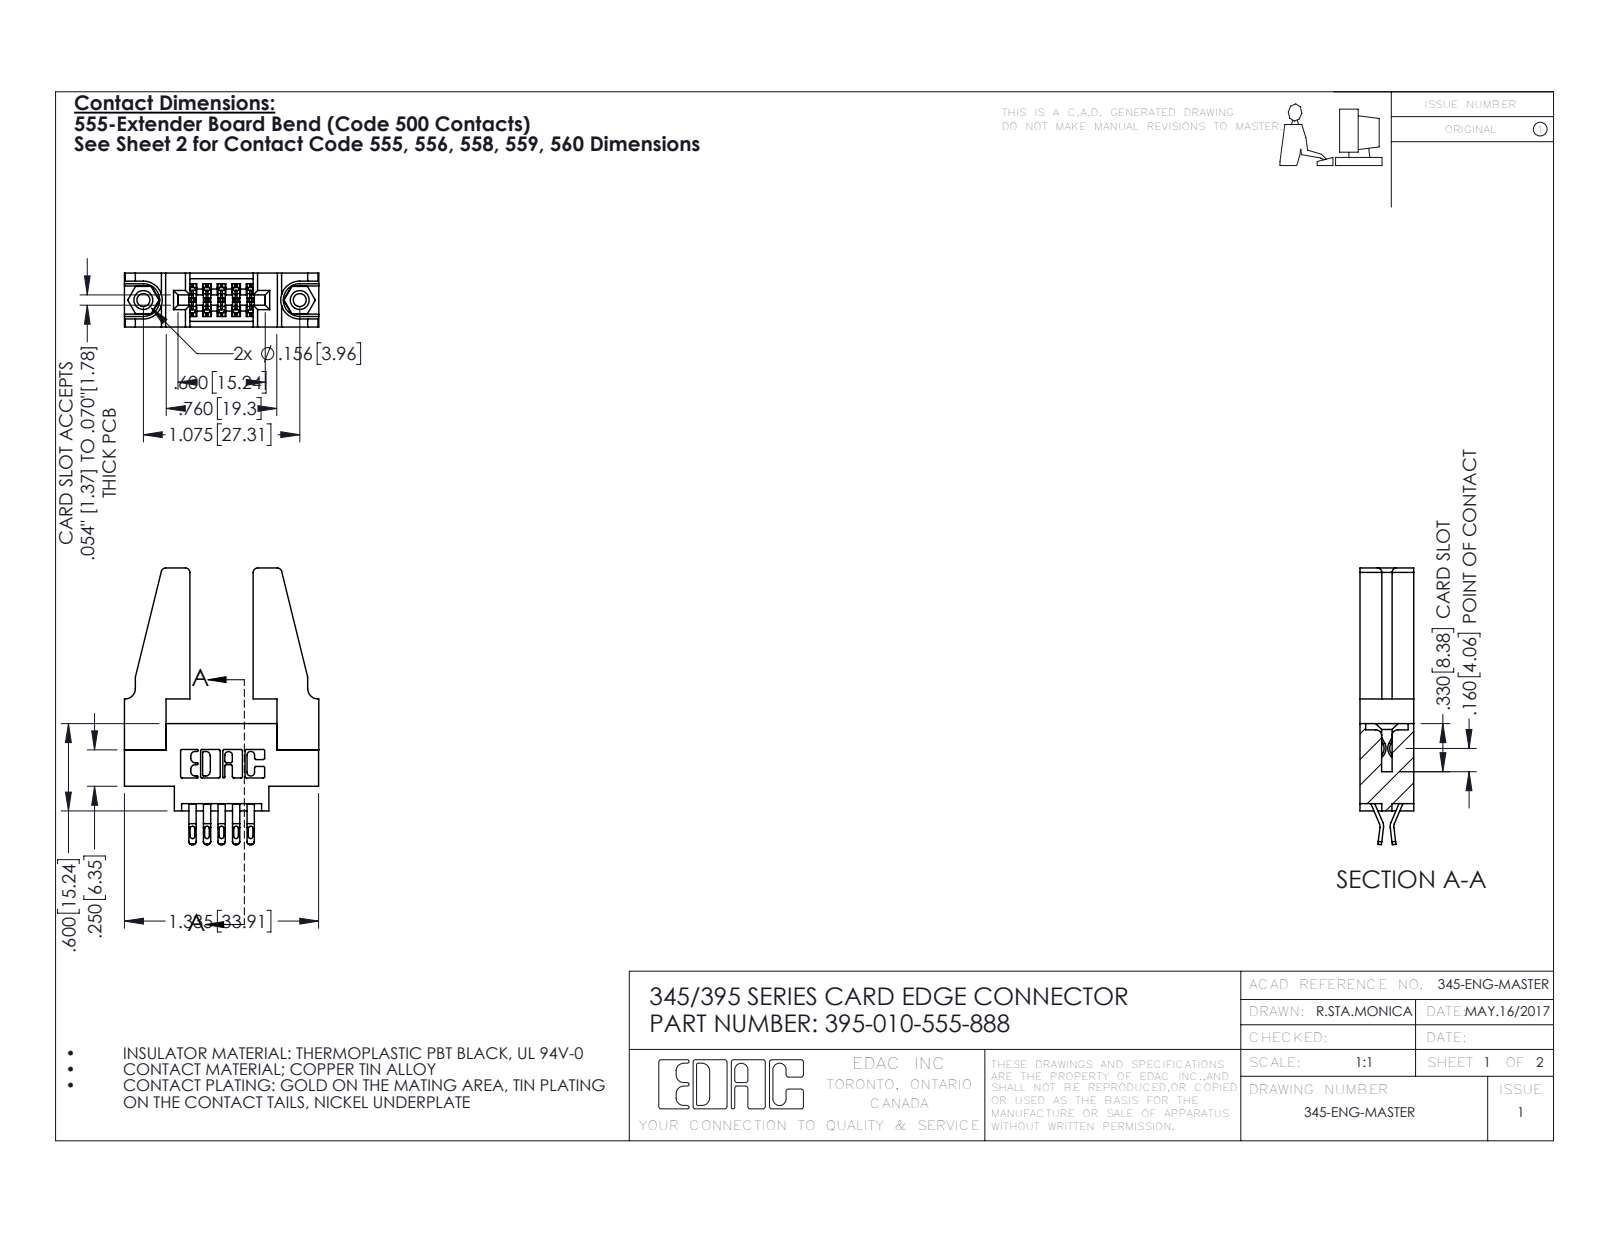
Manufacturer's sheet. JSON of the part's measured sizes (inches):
{"part_name": "345-250-001_345-250-001-102; 345 Part_0.170 Offset - 0.156 Dia-TH; 345-220-078_345-220-088; 395-010-555-888 (+1 more)", "step_written_by": "SolidWorks 2016 (CONFIG_CONTROL_DESIGN)", "units": "inches", "bodies": {"solids": 15, "faces": 814, "planar": 466, "cylindrical": 332, "other": 16}, "overall_size": [1.902, 1.336, 0.37], "volume_in3": 0.374, "surface_area_in2": 10.68, "round_holes": [[0.089, 2], [0.125, 2], [0.156, 2], [0.064, 1]], "round_bosses_or_shafts": [[0.155, 2]], "partial_cylinders_radius": [[0.016, 25], [0.01, 22], [0.02, 20], [0.006, 15], [0.03, 8], [0.007, 6], [0.031, 6], [0.026, 3]], "face_to_face_distances": [0.37, 0.072, 0.298, 0.2, 0.148, 0.15, 0.025, 0.22, 0.077, 0.225], "hole_center_spacings": [0.27, 0.847, 1.075]}
